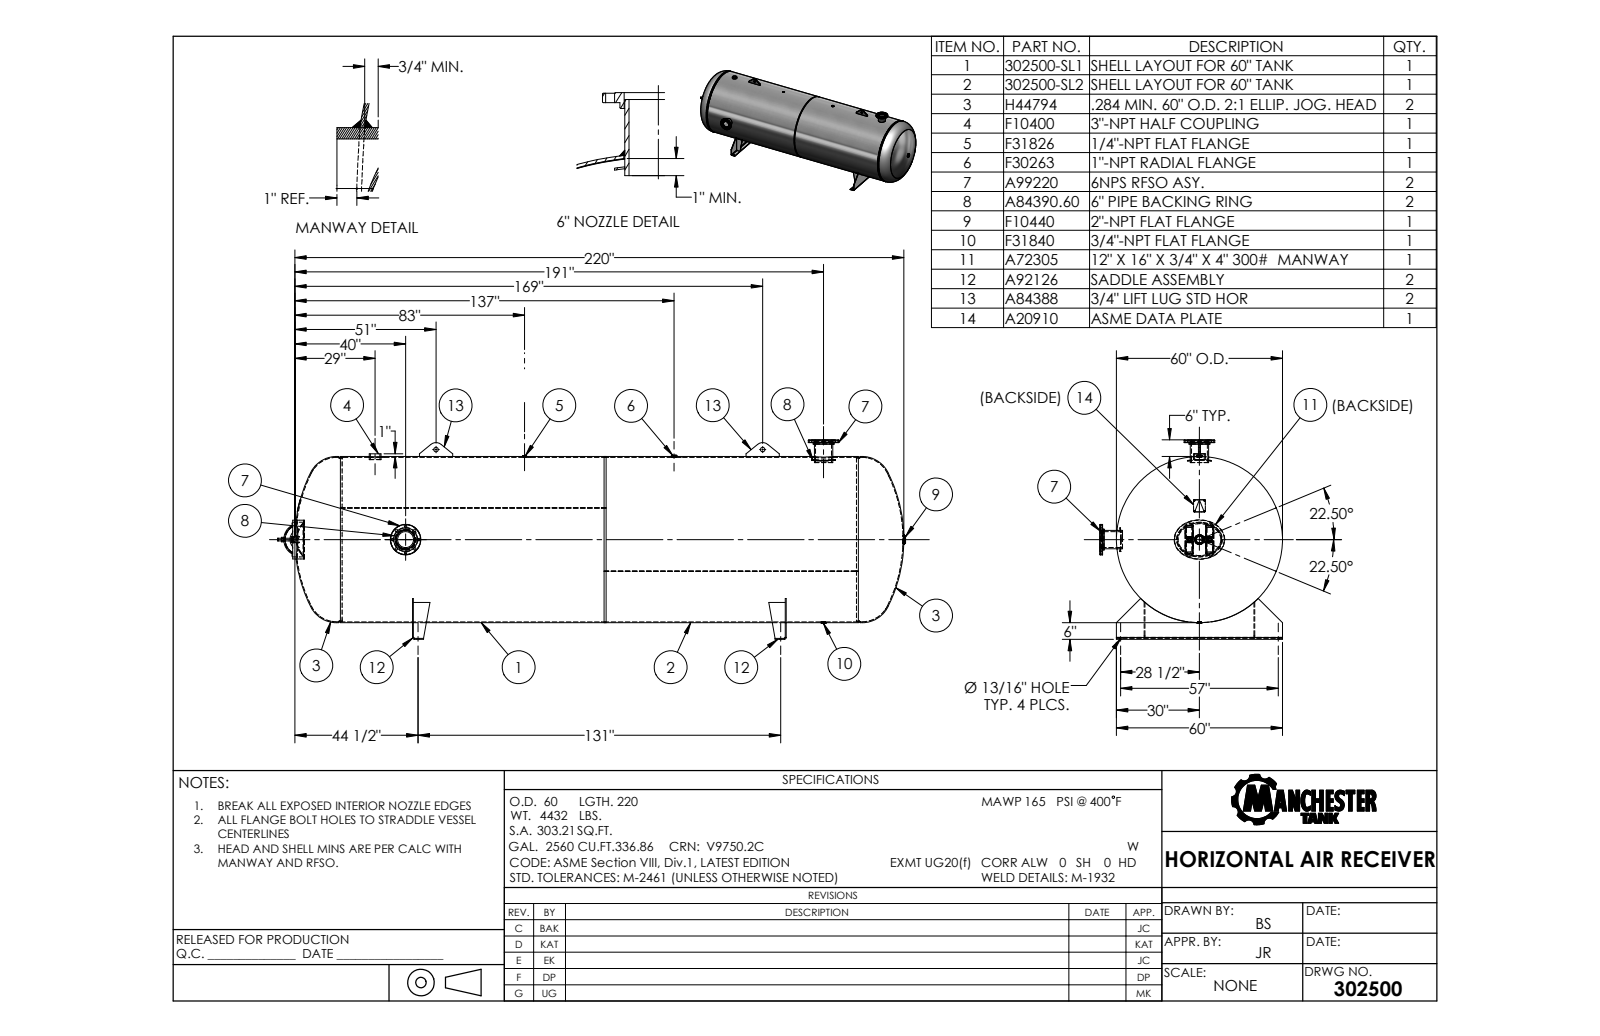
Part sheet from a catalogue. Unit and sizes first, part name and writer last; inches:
Units: inches
Overall size (bounding box): 226.746 × 72 × 66
Round holes (diameter × count): ⌀0.875 ×16, ⌀0.813 ×4, ⌀1.625 ×2, ⌀5.761 ×2, ⌀6.72 ×2, ⌀0.54 ×1, ⌀1.05 ×1, ⌀1.315 ×1, ⌀2.375 ×1, ⌀3.5 ×1, ⌀59.375 ×1
Round bosses / shafts (diameter × count): ⌀11 ×2, ⌀8.5 ×2, ⌀1 ×2, ⌀60 ×1, ⌀6.625 ×1, ⌀6.625 ×1, ⌀4.25 ×1, ⌀3.5 ×1
Partial cylindrical surfaces — rounded edges, fillets, slot ends (radius × count): R1.318 ×4, R0.156 ×2, R0.375 ×2, R0.406 ×2, R3 ×2, R5.917 ×1, R6 ×1, R30.06 ×1
Main face-to-face distances: 0.25, 134.75, 134.5, 135, 0.313, 39.687, 40, 39.375, 19.625, 20.375
Hole centre spacings: 6.718, 3.635, 8.777, 4.75, 3.636, 4.75, 4.75, 8.777
Bodies: 0 solids, 288 faces (107 planar, 122 cylindrical, 59 other)
Part name (STEP PRODUCT): 302500
STEP written by: SolidWorks 2011 (CONFIG_CONTROL_DESIGN)
